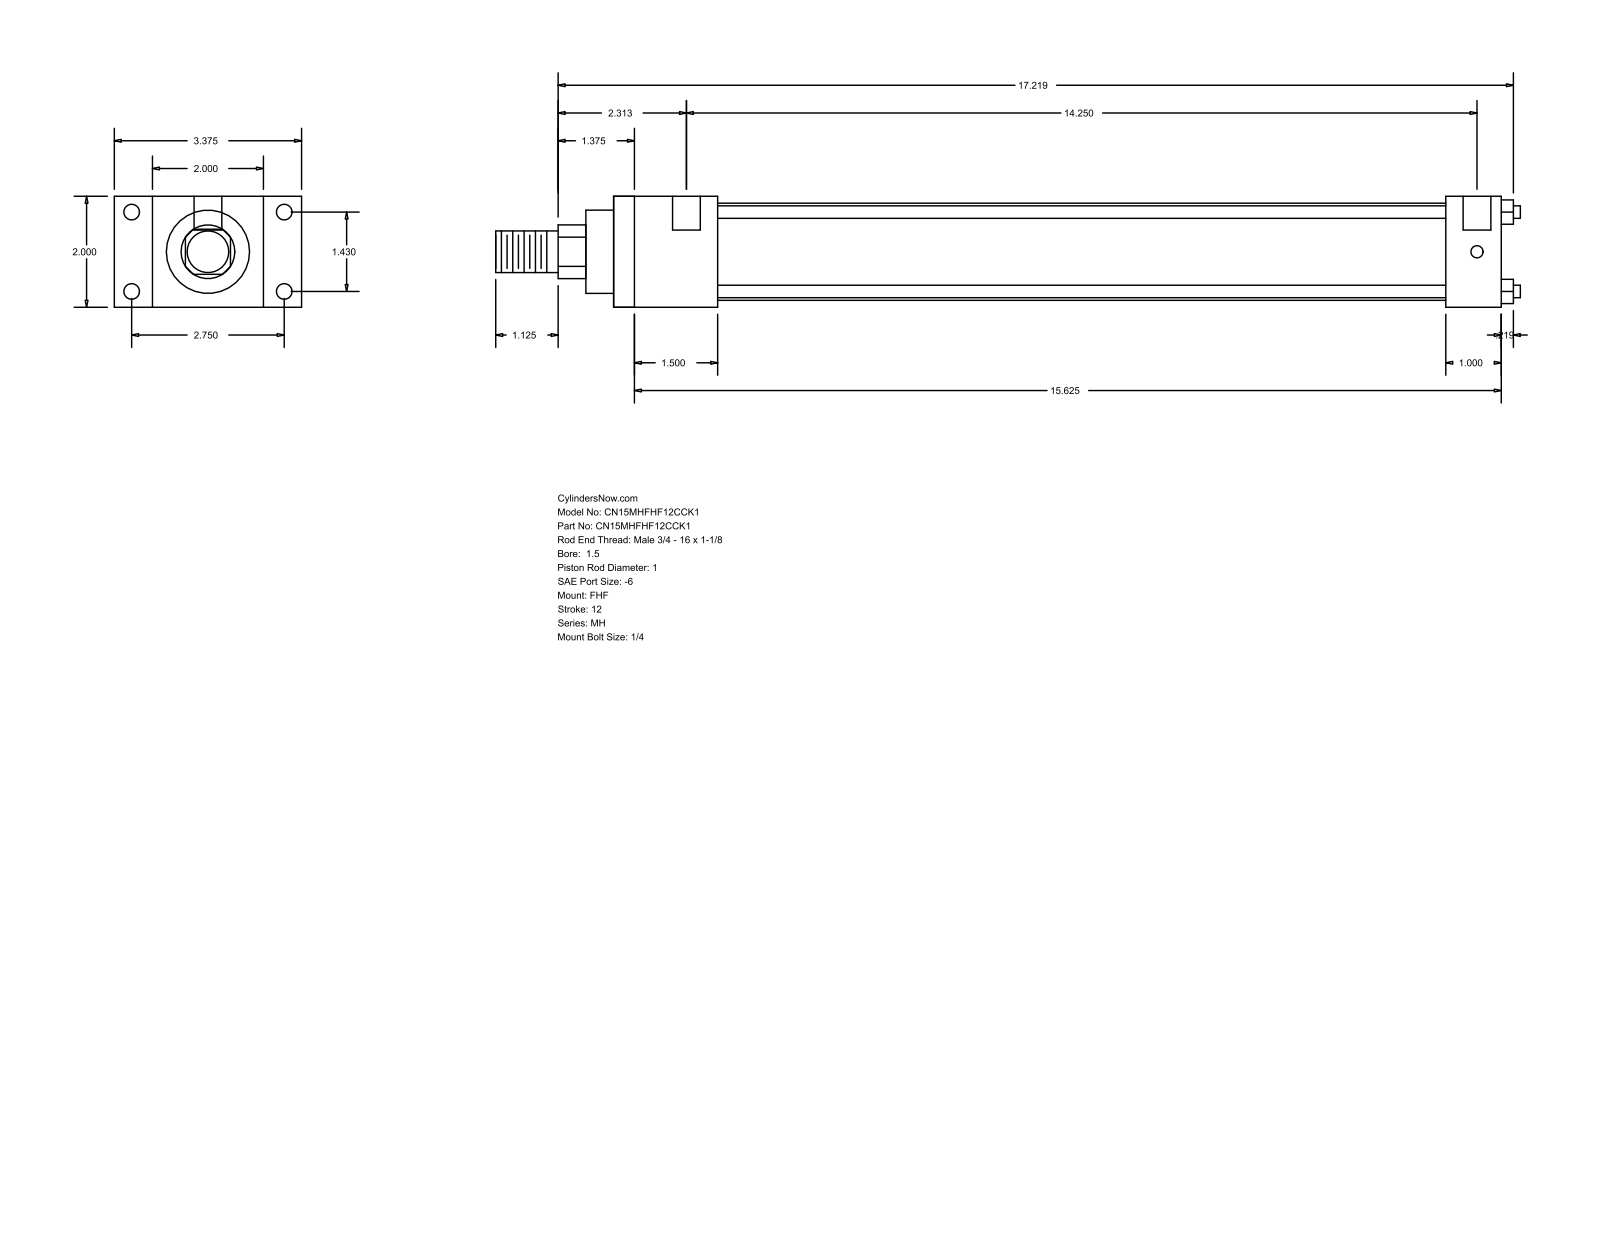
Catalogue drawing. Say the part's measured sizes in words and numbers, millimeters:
The part is named "MH_FHF__0150_1". Its 3-D file was written by "GSSL Pune (CONFIG_CONTROL_DESIGN)". It is 0 solids with 88 faces: 60 planar, 28 cylindrical and 0 other. Overall it measures 469.11 by 85.72 by 50.8 millimeters. Round holes: 4 of diameter 5.56, 4 of diameter 7.14, 2 of diameter 12.7. Round bosses or shafts: 4 of diameter 5.71, 1 of diameter 44.45, 1 of diameter 38.1, 1 of diameter 25.4, 1 of diameter 19.05. Partial cylindrical surfaces (rounded edges, fillets, slot ends): 1 of radius 12.29. The main face-to-face distances are 50.8, 17.46, 68.26, 47.63, 85.72, 406.4, 358.77, 25.4, 381, 333.37. The hole center spacings are 36.32, 69.84, 78.72, 365.13, 3.18, 361.95.
